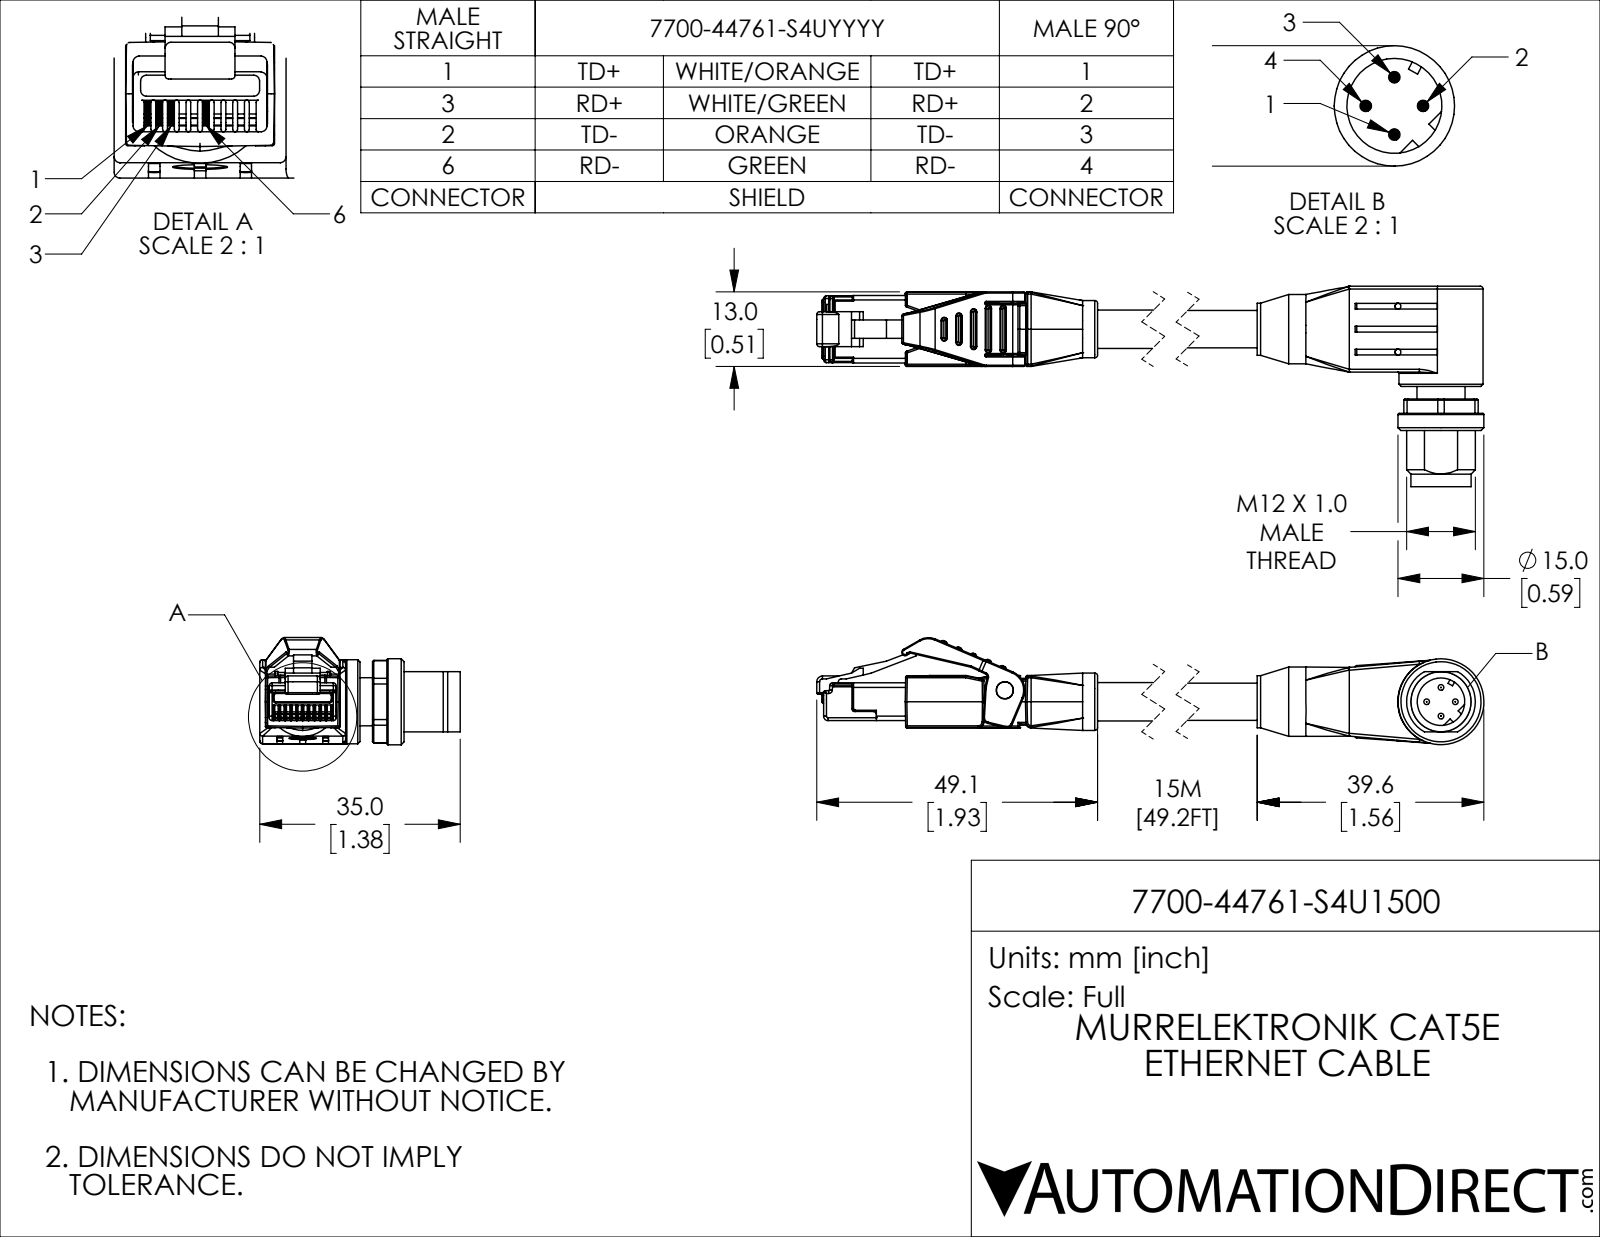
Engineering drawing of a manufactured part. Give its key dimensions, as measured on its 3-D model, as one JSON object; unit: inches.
{"part_name": "7700-44761-S4U1500_2; 7700-44761-S4U1500; 7700-44761-S4U1500_1", "step_written_by": "SolidWorks 2021 (CONFIG_CONTROL_DESIGN)", "units": "inches", "bodies": {"solids": 3, "faces": 883, "planar": 369, "cylindrical": 338, "other": 176}, "overall_size": [5.778, 1.378, 0.736], "volume_in3": 0.915, "surface_area_in2": 11.82, "round_holes": [[0.041, 4], [0.118, 1], [0.189, 1], [0.327, 1]], "round_bosses_or_shafts": [[0.039, 4], [0.591, 1], [0.579, 1], [0.476, 1], [0.413, 1], [0.394, 1], [0.358, 1], [0.331, 1]], "partial_cylinders_radius": [[0.008, 82], [0.012, 67], [0.02, 28], [0.004, 20], [0.031, 5], [0.039, 5], [0.079, 2], [0.197, 2]], "face_to_face_distances": [0.512, 0.362, 0.039, 0.689, 0.098, 0.551, 0.591, 0.185, 0.077, 0.337], "hole_center_spacings": [0.315, 4.19]}
